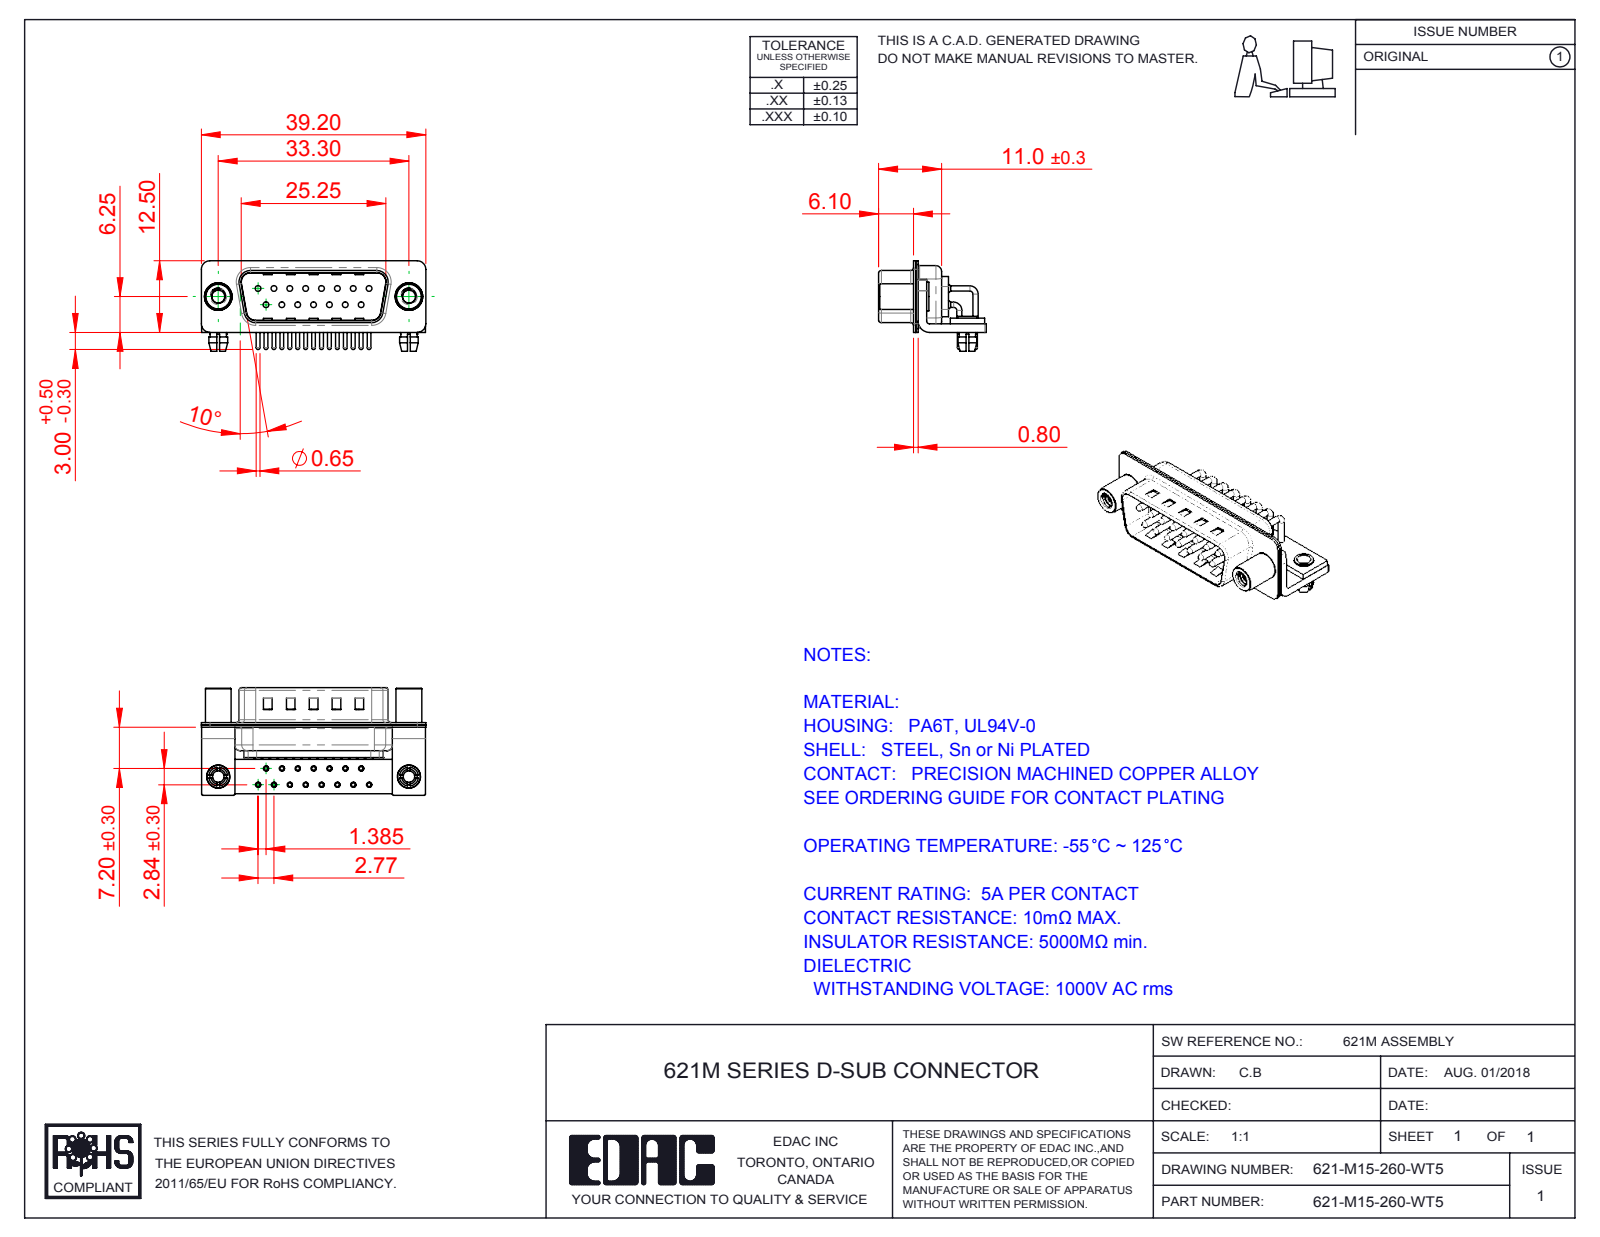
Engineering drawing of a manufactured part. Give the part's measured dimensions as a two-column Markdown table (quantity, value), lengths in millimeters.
| quantity | value |
| --- | --- |
| part name | 621M Stabilizer Board_15 Contacts; 621M Shell Front_15 Contacts; 621M Contact Row 2; 621M 4-40 Threaded Standoff (+6 more) |
| STEP written by | SolidWorks 2016 (CONFIG_CONTROL_DESIGN) |
| units | millimeters |
| bodies | 25 solids, 2212 faces (1175 planar, 799 cylindrical, 238 other) |
| overall size | 39.2 × 18.8 × 15.8 |
| volume | 2 544 mm³ |
| surface area | 6 913 mm² |
| round holes (diameter × count) | 2 × 17, 0.9 × 15, 1 × 15, 1.7 × 15, 2.26 × 2, 2.5 × 2, 3.2 × 2, 4 × 2, 4.8 × 2 |
| round bosses / shafts (diameter × count) | 0.9 × 22, 1.5 × 15, 0.65 × 15, 5 × 2, 4.9 × 2, 4.5 × 2, 4 × 2, 3.4 × 2 |
| partial cylindrical surfaces (radius × count) | 0.25 × 16, 1.5 × 16, 1.01 × 15, 2 × 13, 0.5 × 9, 1.6 × 8, 0.6 × 4, 0.65 × 4 |
| main face-to-face distances | 0.4, 0.85, 1.5, 0.8, 1.25, 10.4, 9.55, 1, 1.9, 8.3 |
| hole center spacings | 3.16, 2.77, 5.54, 8.31, 11.08, 5.03, 5.04, 7.48 |
